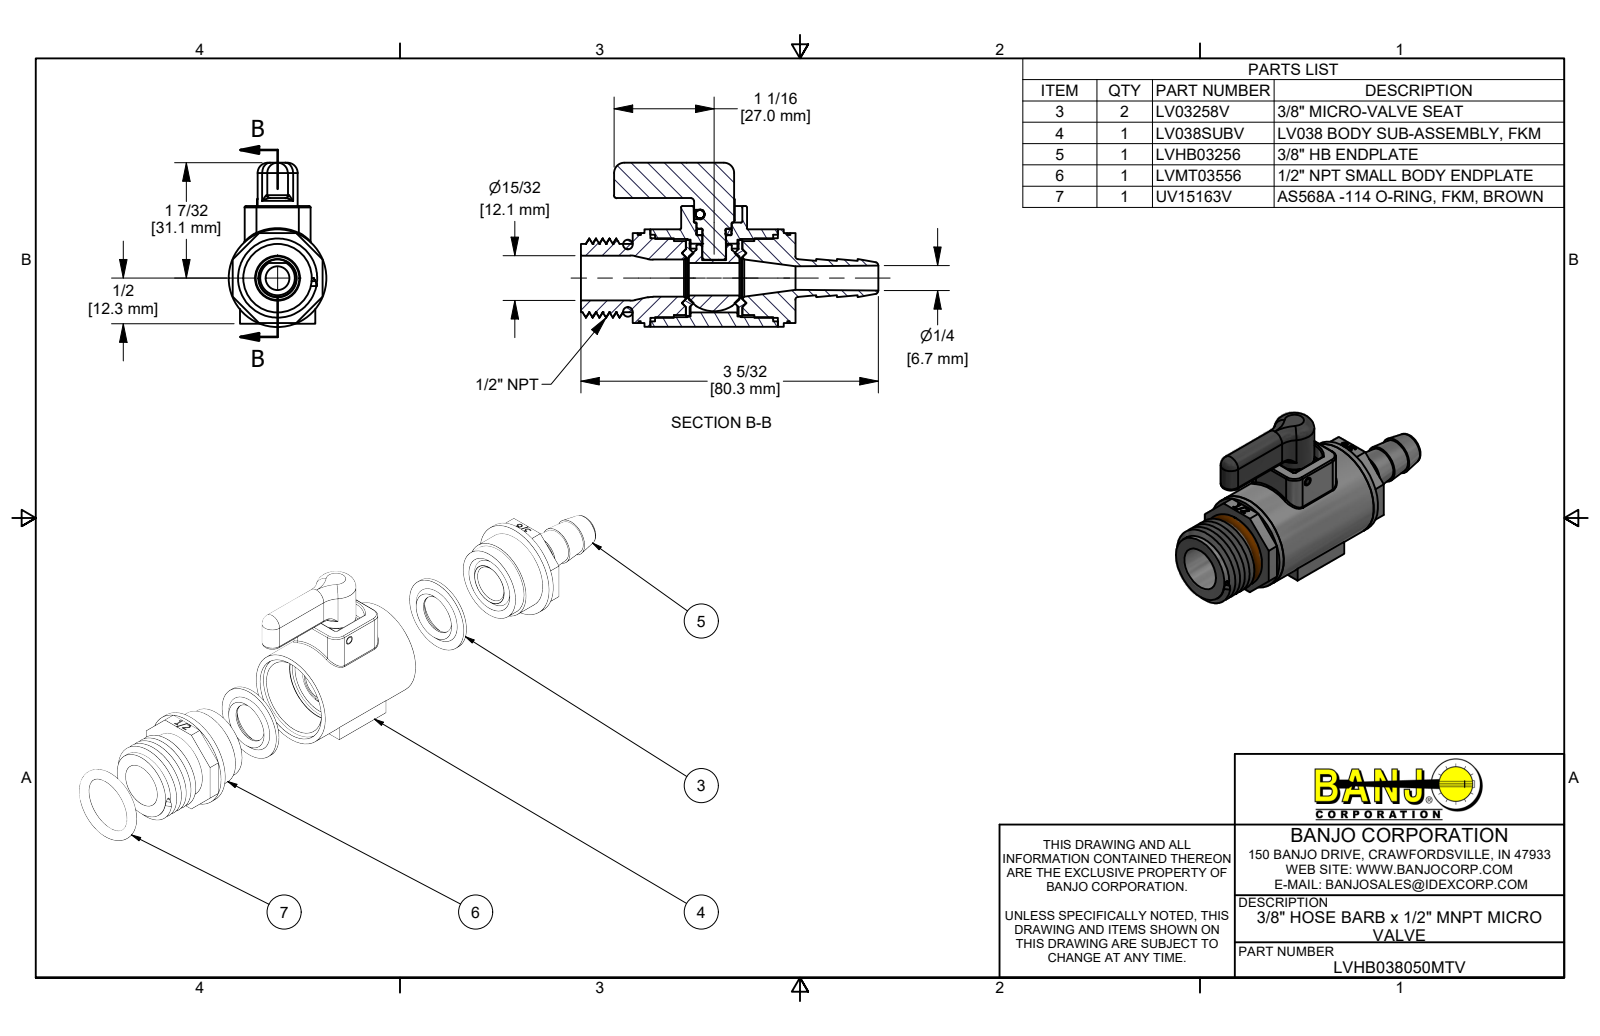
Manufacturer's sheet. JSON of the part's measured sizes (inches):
{"part_name": "LVHB038050MTV; LV038SUBV; LV03254A; AQ010V (+7 more)", "step_written_by": "Autodesk Inventor 2012 (AUTOMOTIVE_DESIGN)", "units": "inches", "bodies": {"solids": 9, "faces": 676, "planar": 280, "cylindrical": 106, "other": 290}, "overall_size": [3.16, 1.743, 1.035], "volume_in3": 1.256, "surface_area_in2": 30.21, "round_holes": [[0.093, 1], [0.251, 1], [0.368, 1], [0.37, 1], [0.376, 1], [0.395, 1], [0.421, 1], [0.476, 1], [0.73, 1], [0.815, 1], [0.83, 1], [0.92, 1]], "round_bosses_or_shafts": [[1.035, 1], [0.845, 1], [0.812, 1], [0.785, 1], [0.726, 1], [0.425, 1], [0.375, 1], [0.372, 1]], "partial_cylinders_radius": [[0.01, 16], [0.015, 14], [0.125, 4], [0.03, 2], [0.05, 2], [0.109, 2], [0.25, 2], [0.048, 1]], "face_to_face_distances": [0.977, 0.377, 0.188, 1.542, 1.165, 0.565, 0.05, 0.327, 1.354, 0.04]}
